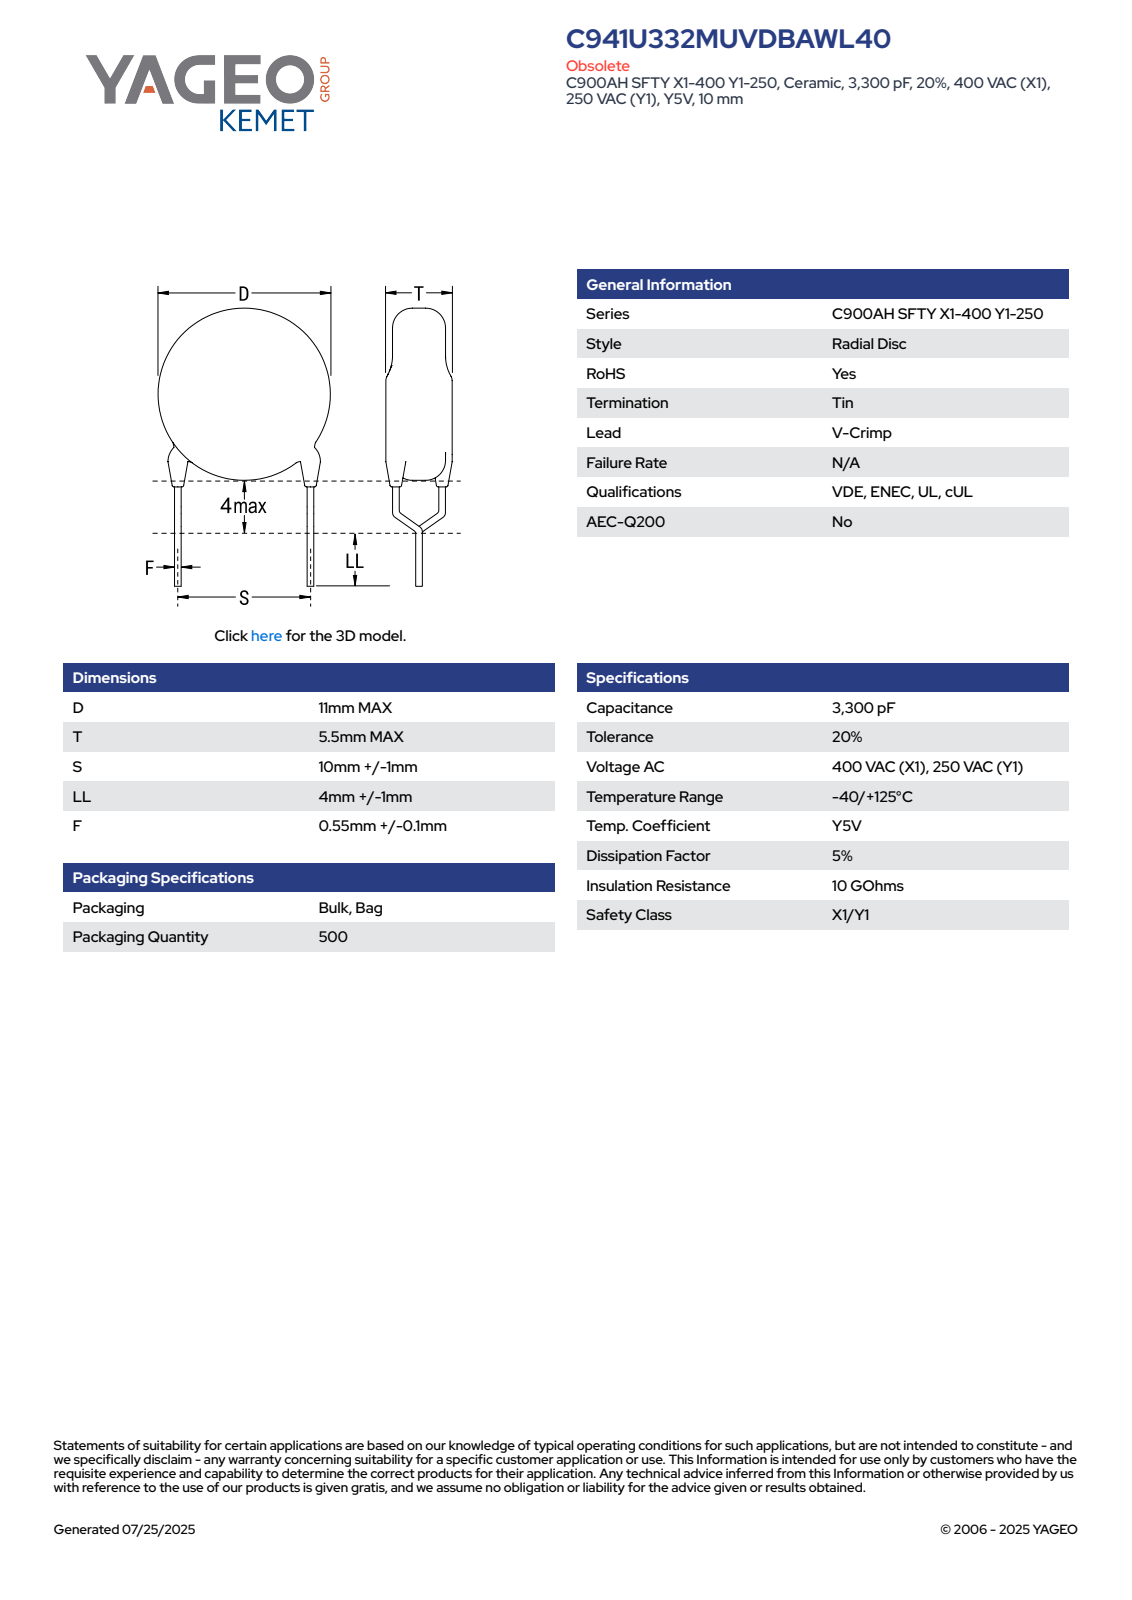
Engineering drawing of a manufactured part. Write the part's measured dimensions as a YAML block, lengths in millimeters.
part_name: "CCD_VCC900_D11T5.5S10LL5F0.65"
step_written_by: "SolidWorks 2014 (AUTOMOTIVE_DESIGN)"
units: millimeters
bodies: {solids: 5, faces: 93, planar: 65, cylindrical: 16, other: 12}
overall_size: [19.8, 11, 5.5]
volume: 518
surface_area: 412
round_bosses_or_shafts:
  - {diameter: 0.65, count: 6}
  - {diameter: 11, count: 1}
face_to_face_distances: [5.5, 7.9, 15.01, 7.11, 13.58, 5.68, 1.43, 0.39, 0.35, 5.84]
